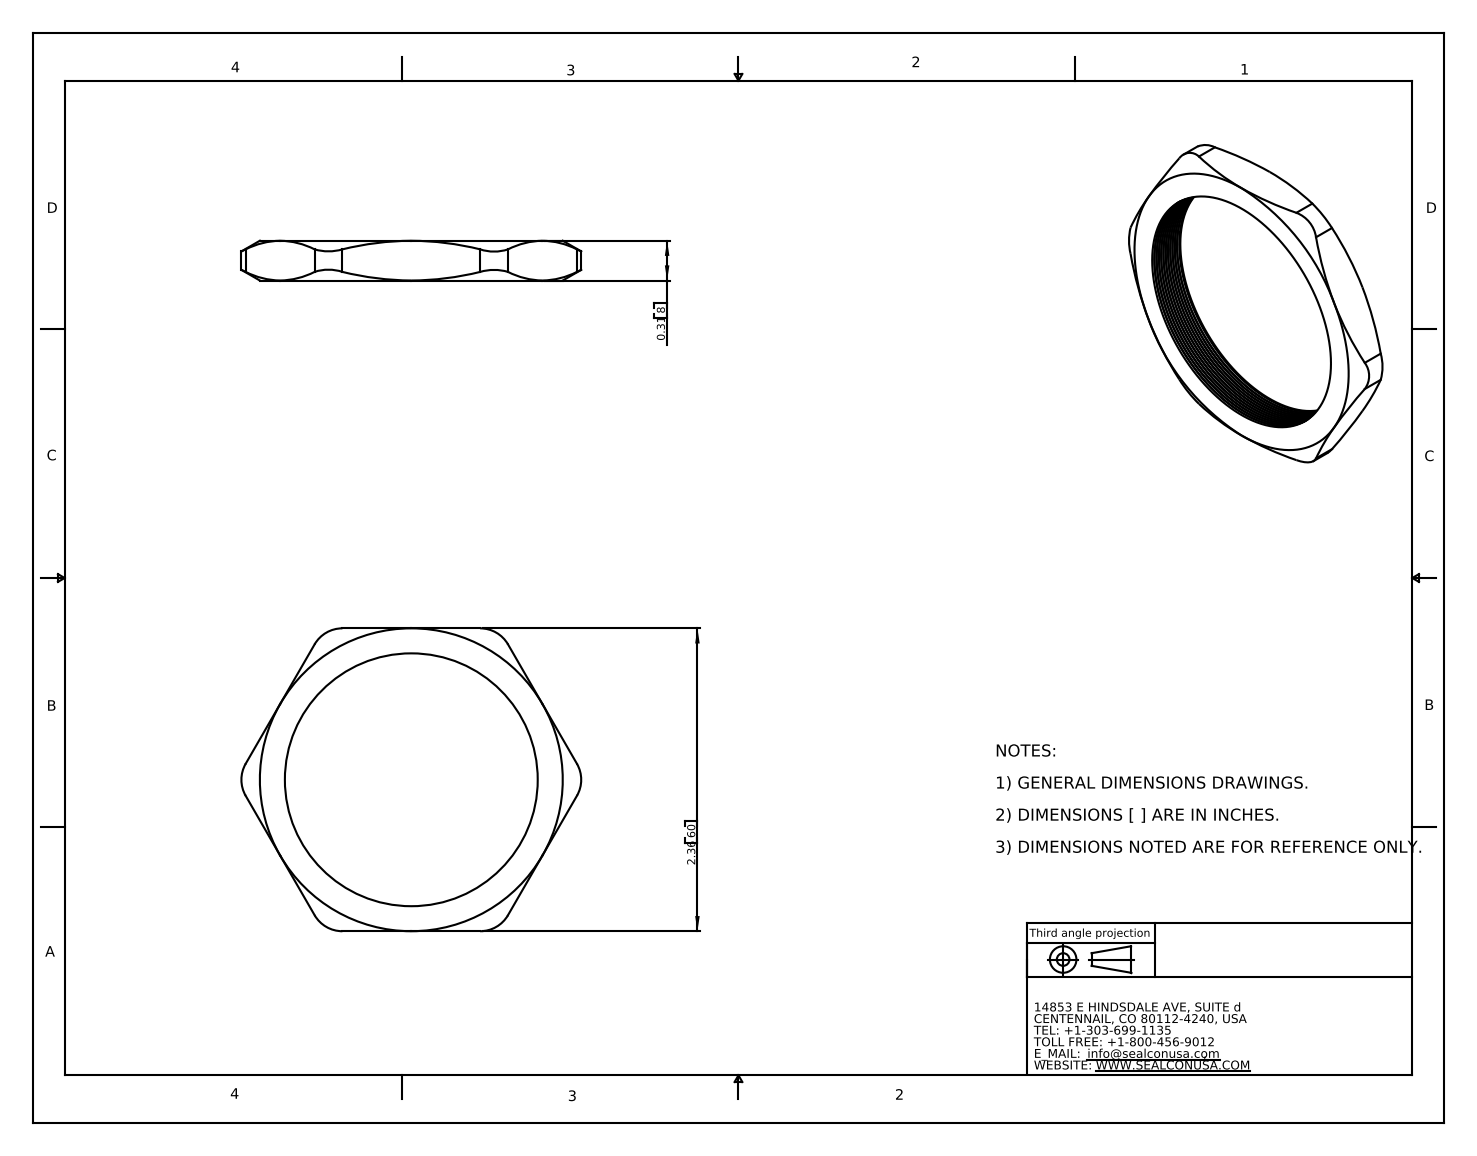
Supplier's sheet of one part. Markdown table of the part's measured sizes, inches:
| quantity | value |
| --- | --- |
| part name | NM-50-GY |
| STEP written by | SolidWorks 2007 (CONFIG_CONTROL_DESIGN) |
| units | inches |
| bodies | 1 solid, 101 faces (8 planar, 31 cylindrical, 62 other) |
| overall size | 2.648 × 2.36 × 0.31 |
| volume | 0.502 in³ |
| surface area | 9.258 in² |
| round holes (diameter × count) | 1.97 × 1 |
| partial cylindrical surfaces (radius × count) | 0.25 × 6 |
| main face-to-face distances | 0.31, 2.36 |
